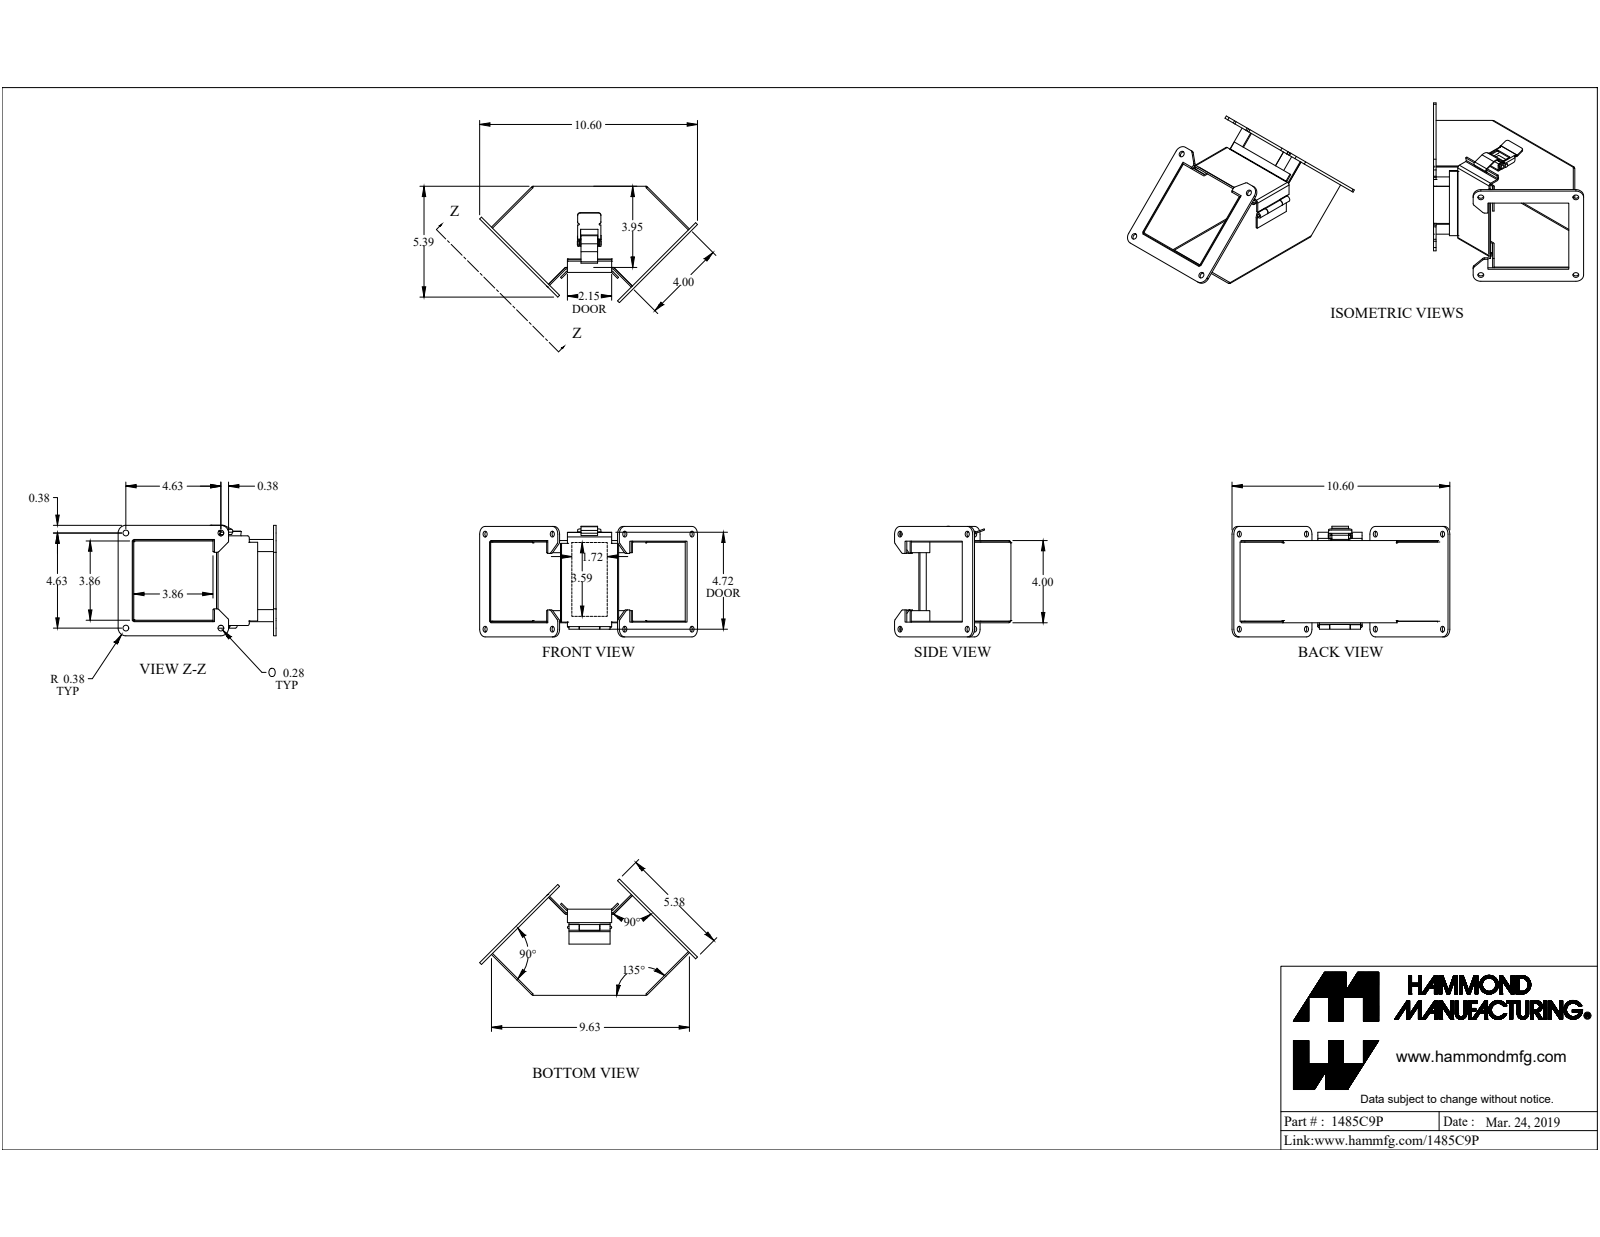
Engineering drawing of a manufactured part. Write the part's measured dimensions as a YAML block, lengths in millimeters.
part_name: "1485C9P"
step_written_by: "SolidWorks 2019 (CONFIG_CONTROL_DESIGN)"
units: millimeters
bodies: {solids: 12, faces: 333, planar: 222, cylindrical: 109, other: 2}
overall_size: [269.2, 143.8, 136.7]
volume: 204800
surface_area: 216500
round_holes:
  - {diameter: 7.1, count: 8}
  - {diameter: 3.2, count: 1}
  - {diameter: 3.3, count: 1}
  - {diameter: 4.2, count: 1}
round_bosses_or_shafts:
  - {diameter: 4.7, count: 2}
  - {diameter: 7, count: 1}
  - {diameter: 4, count: 1}
  - {diameter: 3.2, count: 1}
partial_cylinders:
  - {radius: 0.9, count: 11}
  - {radius: 2.7, count: 11}
  - {radius: 3.2, count: 11}
  - {radius: 9.5, count: 8}
  - {radius: 0.4, count: 7}
  - {radius: 0.9, count: 3}
  - {radius: 1, count: 3}
  - {radius: 1.9, count: 3}
face_to_face_distances: [1.8, 99.8, 101.6, 97.9, 172.8, 174.6, 104.6, 3.2, 175.9, 177.8]
hole_center_spacings: [117.5, 166.1, 117.5, 7.2, 112.5, 113.3]
